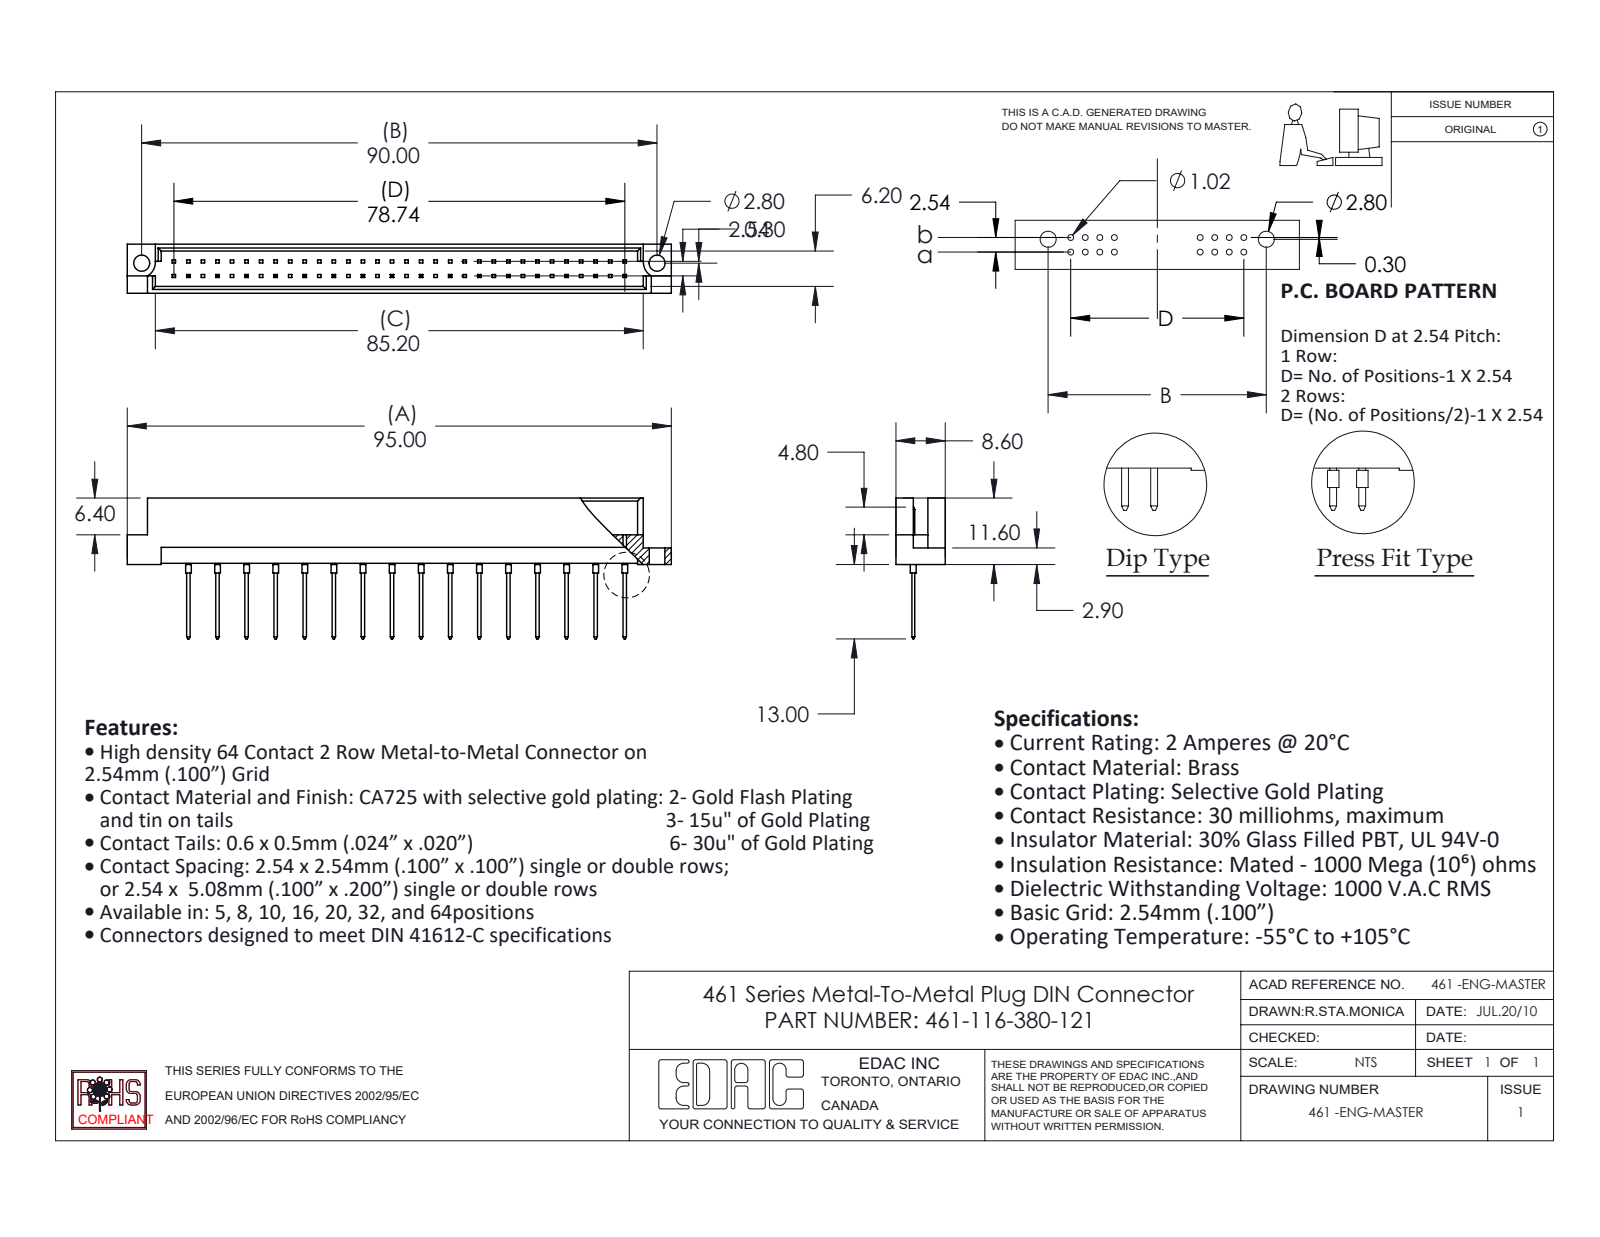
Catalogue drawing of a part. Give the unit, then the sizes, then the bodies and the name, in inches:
Units: inches
Overall size (bounding box): 3.74 × 0.969 × 0.339
Round holes (diameter × count): ⌀0.11 ×2
Round bosses / shafts (diameter × count): ⌀0.039 ×16
Partial cylindrical surfaces — rounded edges, fillets, slot ends (radius × count): R0.11 ×2
Main face-to-face distances: 0.047, 0.291, 0.339, 0.244, 0.197, 0.129, 0.209, 0.082, 0.162, 0.109
Hole centre spacings: 3.543
Volume: 0.292 in³ · Surface area: 10.1 in²
Bodies: 17 solids, 657 faces (618 planar, 39 cylindrical, 0 other)
Part name (STEP PRODUCT): 461-290_80; 461-116-380-121; 461 Part_64
STEP written by: SolidWorks 2020 (CONFIG_CONTROL_DESIGN)
